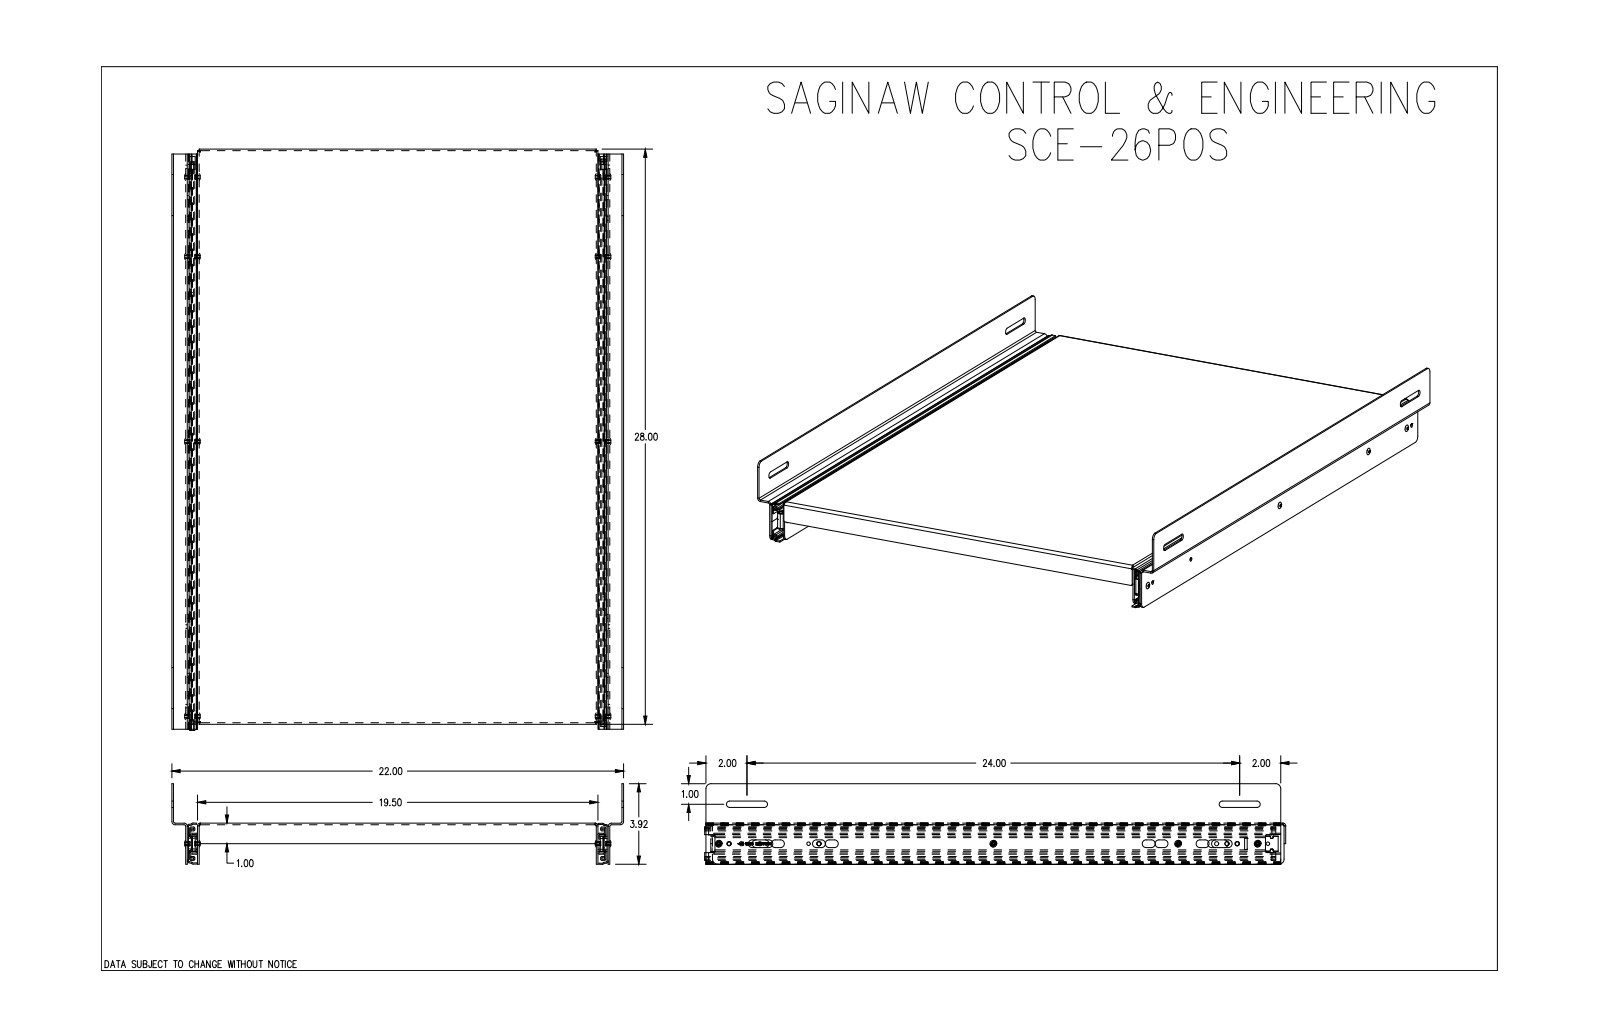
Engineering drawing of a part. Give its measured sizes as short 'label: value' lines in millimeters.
name: SCE-26POS
written by: SolidWorks 2021 (AUTOMOTIVE_DESIGN)
unit: mm
bodies: 25 solids, 584 faces (288 planar, 248 cylindrical, 48 other)
size: 718.8 × 558.8 × 99.8
volume: 1 541 000 mm³; area: 1 707 000 mm²
holes: 25× ⌀5.1, 11× ⌀4.4, 8× ⌀2.5
bosses: 8× ⌀5.6, 8× ⌀4.1
rounds: 20× R0.8, 19× R4.8, 16× R1.6, 4× R0.5, 4× R0.9, 4× R1, 4× R1, 4× R1.3
face distances: 2, 508, 31.8, 14.7, 17.1, 525.1, 539.8, 12.7, 1.4, 506
hole spacings: 12.7, 628.7, 12.6, 12.8, 25.4, 38, 38.1, 111.1
